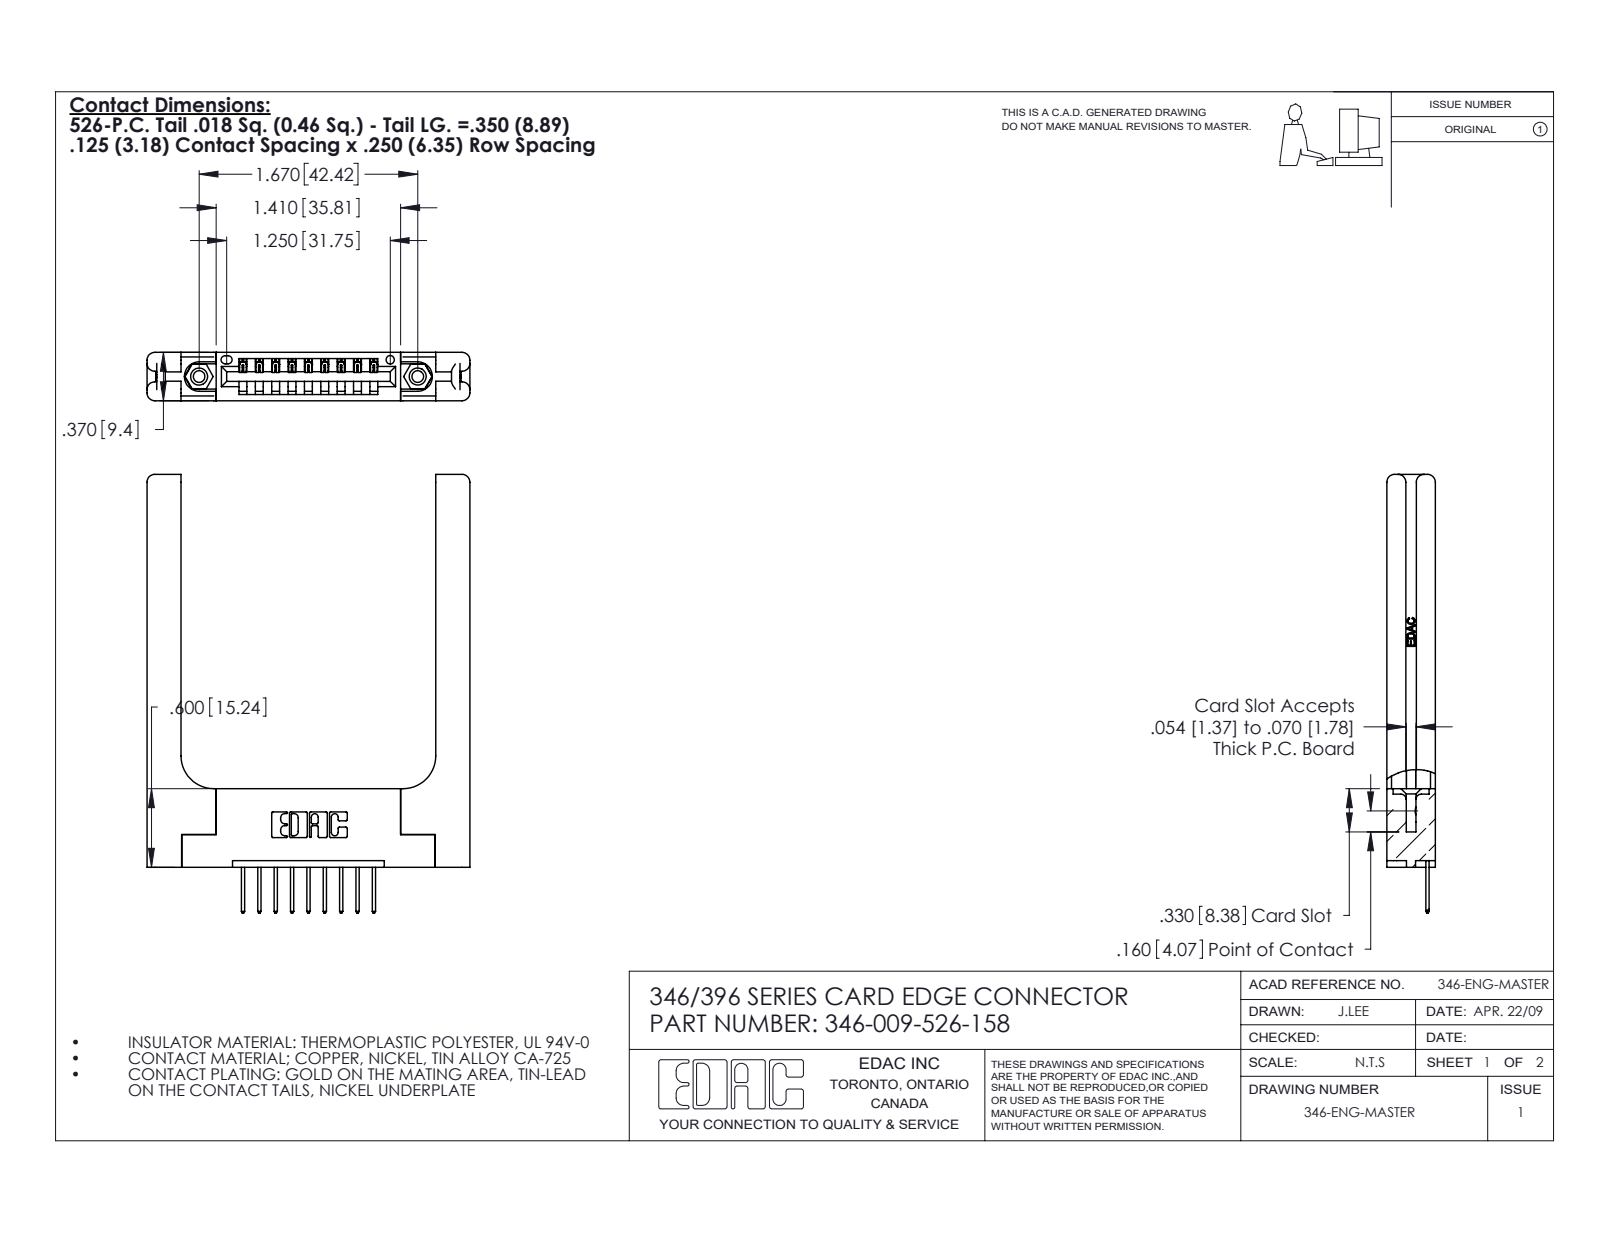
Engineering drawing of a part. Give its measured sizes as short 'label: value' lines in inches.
name: 345-250-001_345-250-001-102; 346-220-058_345-220-058; 346 Part_Flush Mounting Lugs - 0.156 Dia-TH; 345-292-001_345-293-126 (+1 more)
written by: SolidWorks 2020 (CONFIG_CONTROL_DESIGN)
unit: in
bodies: 14 solids, 914 faces (598 planar, 256 cylindrical, 60 other)
size: 3.35 × 2.466 × 0.37
volume: 0.809 in³; area: 18.62 in²
holes: 2× ⌀0.089, 2× ⌀0.125, 2× ⌀0.156, 1× ⌀0.064
bosses: 2× ⌀0.155
rounds: 22× R0.01, 18× R0.006, 18× R0.01, 16× R0.06, 6× R0.007, 6× R0.031, 3× R0.026, 2× R0.03
face distances: 0.37, 0.15, 0.22, 0.072, 0.148, 0.25, 0.048, 0.322, 0.102, 0.173
hole spacings: 0.246, 1.465, 1.67
